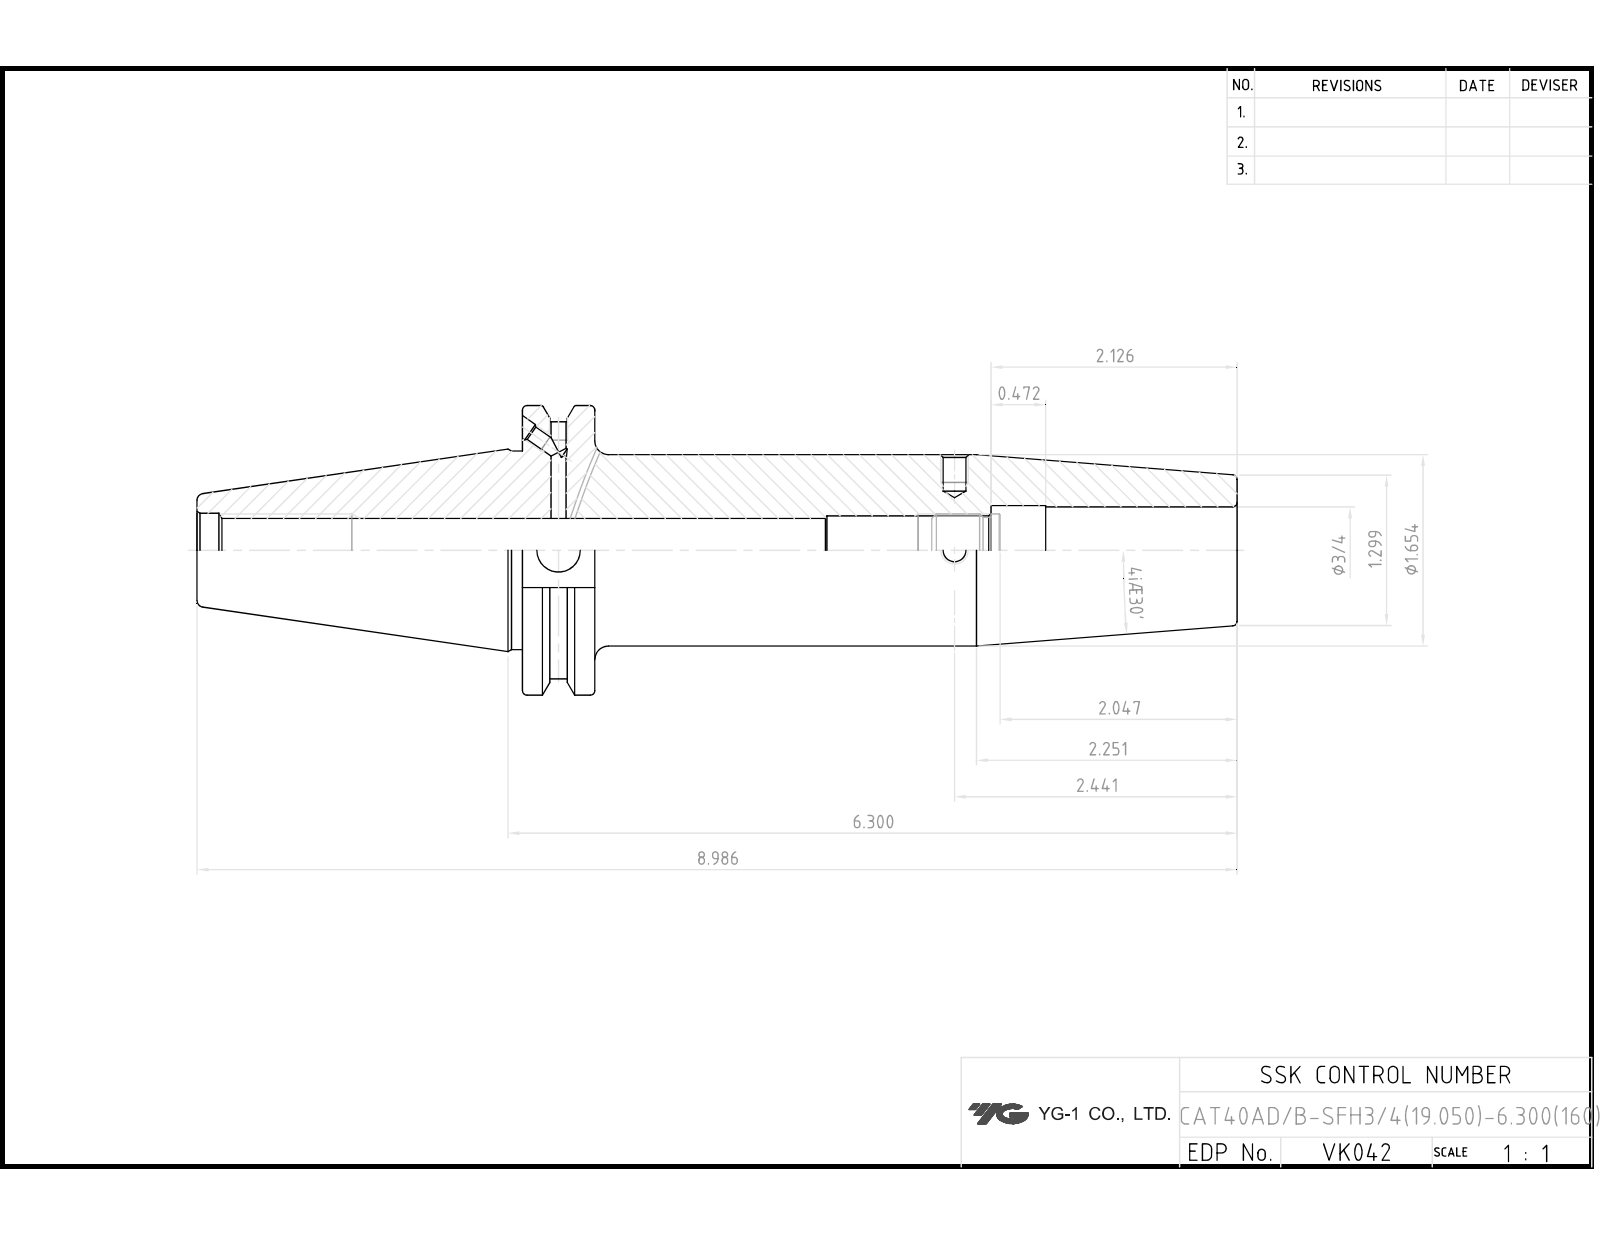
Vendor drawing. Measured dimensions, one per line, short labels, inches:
name: LO-CAT40ADB-SFH19.05-160
written by: Autodesk Inventor 2022 (AUTOMOTIVE_DESIGN)
unit: in
bodies: 1 solid, 87 faces (37 planar, 29 cylindrical, 21 other)
size: 8.986 × 2.5 × 2.405
volume: 15.36 in³; area: 69.47 in²
holes: 4× ⌀0.128, 2× ⌀0.157, 2× ⌀0.165, 1× ⌀0.375, 1× ⌀0.512, 1× ⌀0.527, 1× ⌀0.587, 1× ⌀0.642, 1× ⌀0.75, 1× ⌀0.797
bosses: 1× ⌀2.5, 1× ⌀1.717, 1× ⌀1.654
rounds: 1× R1.108
face distances: 0.625, 6.174, 5.549, 1.874, 0.645, 4.048, 3.423, 2.126, 2.812, 3.437
